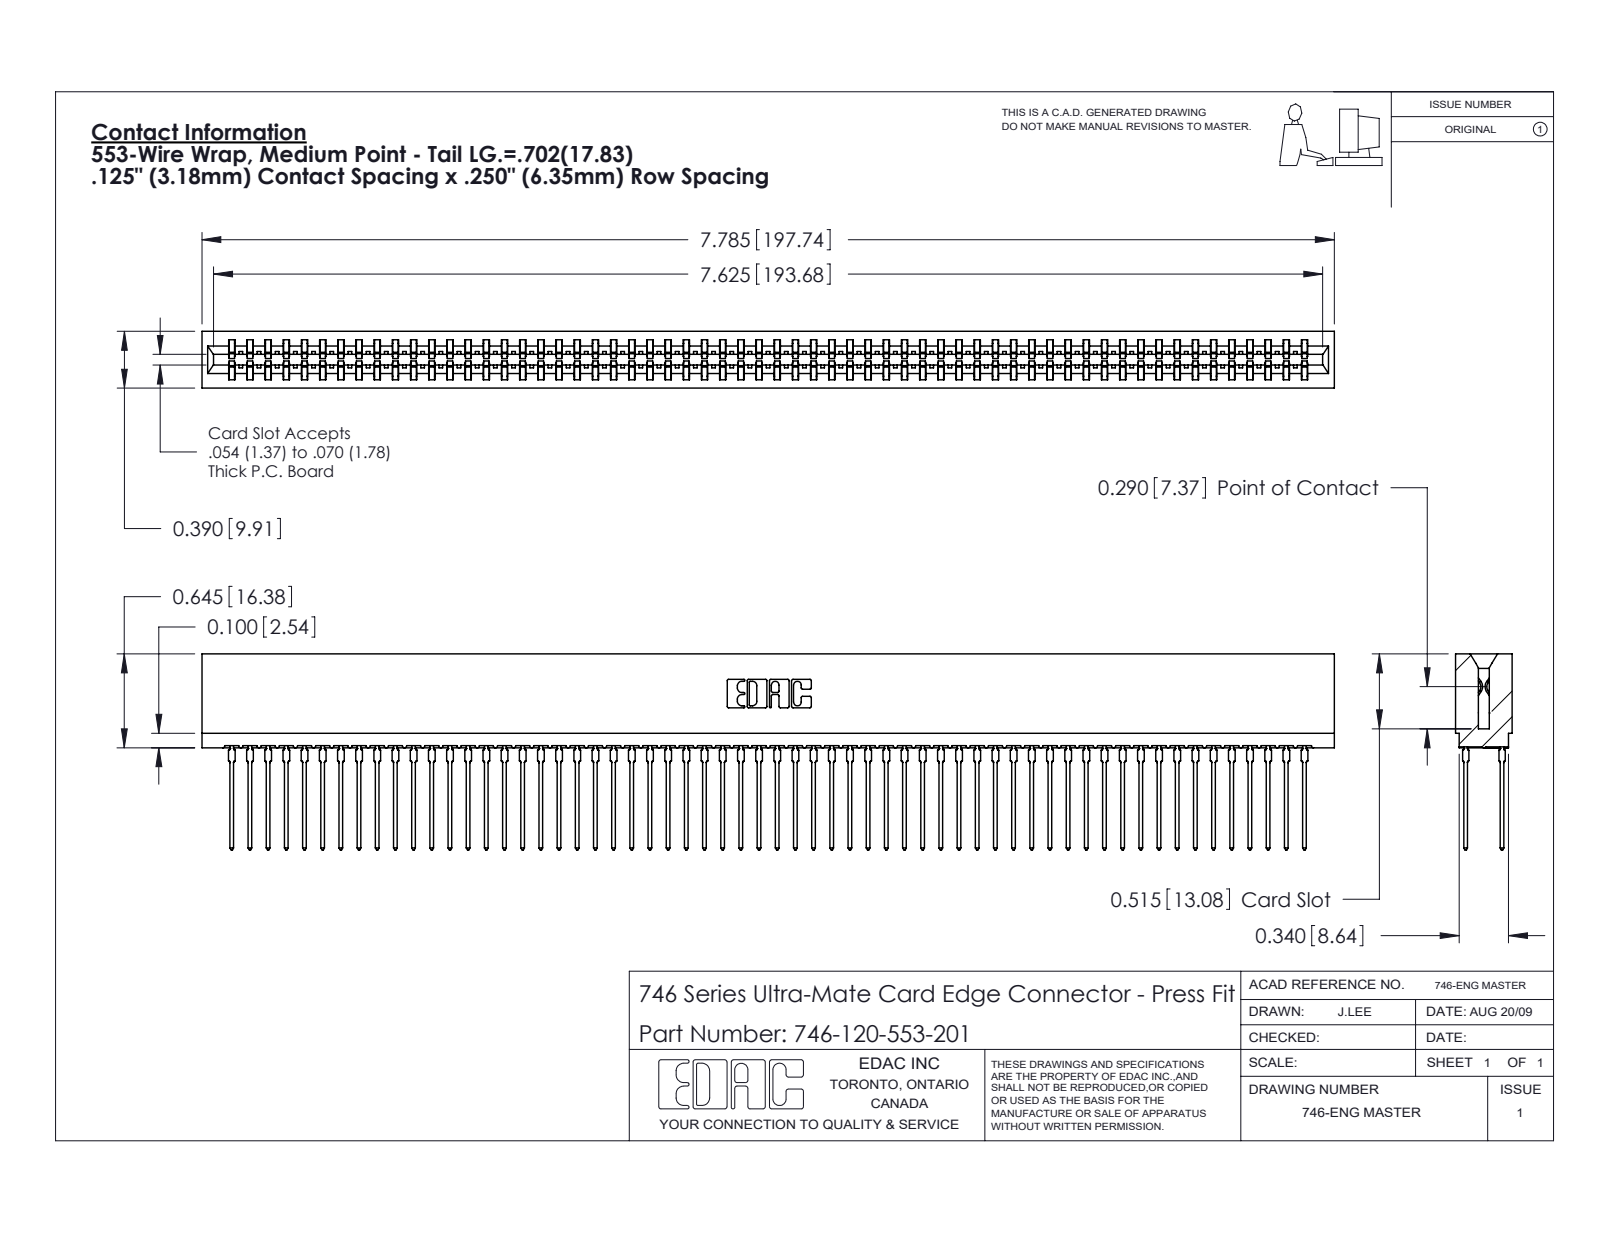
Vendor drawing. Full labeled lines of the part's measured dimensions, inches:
Part name (STEP PRODUCT): 746-120-553-201; 746-292-001_553; 746 Part_.515 Slot Depth - 01
STEP written by: SolidWorks 2020 (CONFIG_CONTROL_DESIGN)
Units: inches
Bodies: 121 solids, 10837 faces (5575 planar, 2142 cylindrical, 3120 other)
Overall size (bounding box): 7.785 × 1.346 × 0.39
Volume: 1.319 in³ · Surface area: 58.14 in²
Partial cylindrical surfaces — rounded edges, fillets, slot ends (radius × count): R0.021 ×240, R0.015 ×61, R0.01 ×22, R0.005 ×8, R0.011 ×8, R0.007 ×6, R0.031 ×6, R0.026 ×3
Main face-to-face distances: 0.057, 0.333, 0.025, 0.25, 0.307, 0.39, 0.083, 0.275, 0.174, 0.158
